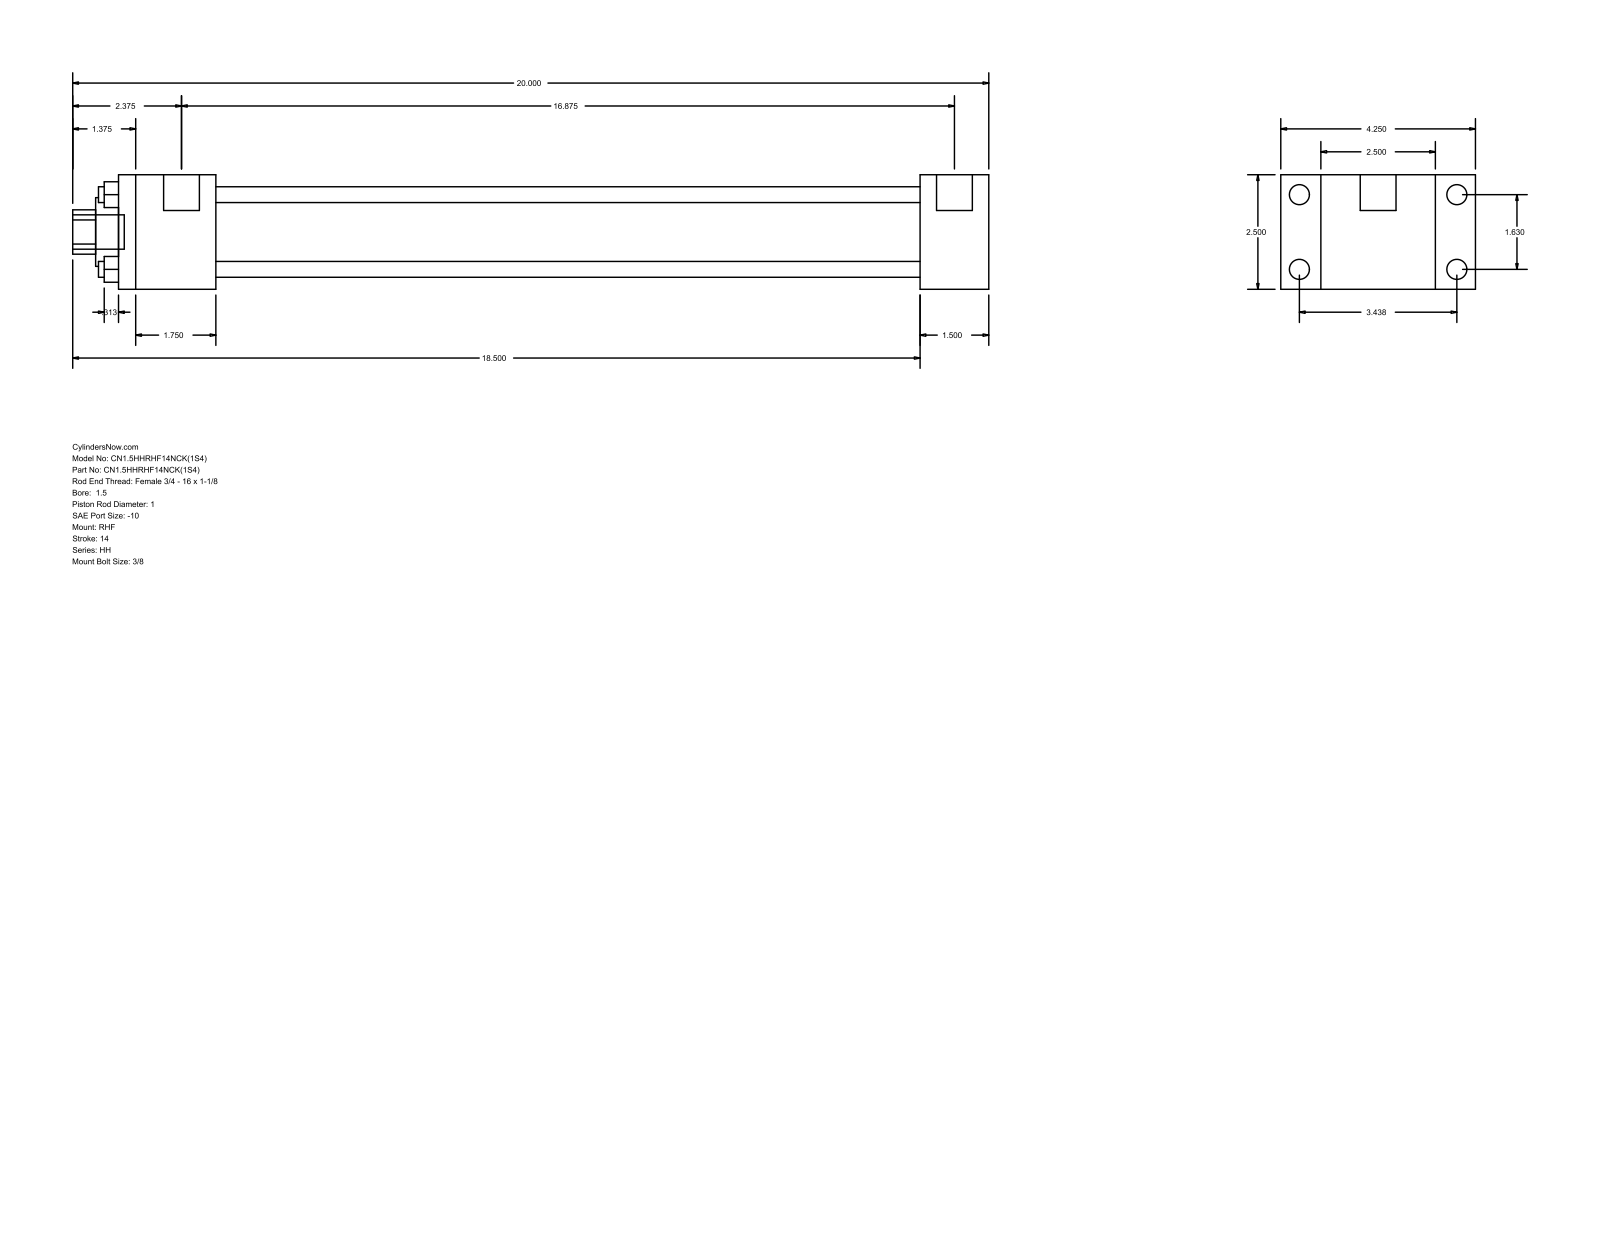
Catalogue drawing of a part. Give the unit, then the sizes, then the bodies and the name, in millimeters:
Units: millimetres
Overall size (bounding box): 508 × 107.95 × 63.5
Round holes (diameter × count): ⌀8.76 ×4, ⌀25.4 ×1, ⌀38.1 ×1, ⌀44.45 ×1
Round bosses / shafts (diameter × count): ⌀11.13 ×4, ⌀5.56 ×4, ⌀19.84 ×2, ⌀19.05 ×1
Partial cylindrical surfaces — rounded edges, fillets, slot ends (radius × count): R12.29 ×1
Main face-to-face distances: 63.5, 22.23, 85.73, 38.1, 107.96, 390.52, 428.62, 53.98, 444.5, 482.6
Hole centre spacings: 29.27, 41.4, 58.55
Bodies: 0 solids, 88 faces (60 planar, 28 cylindrical, 0 other)
Part name (STEP PRODUCT): HH_RHF__0150_1
STEP written by: GSSL Pune (CONFIG_CONTROL_DESIGN)
